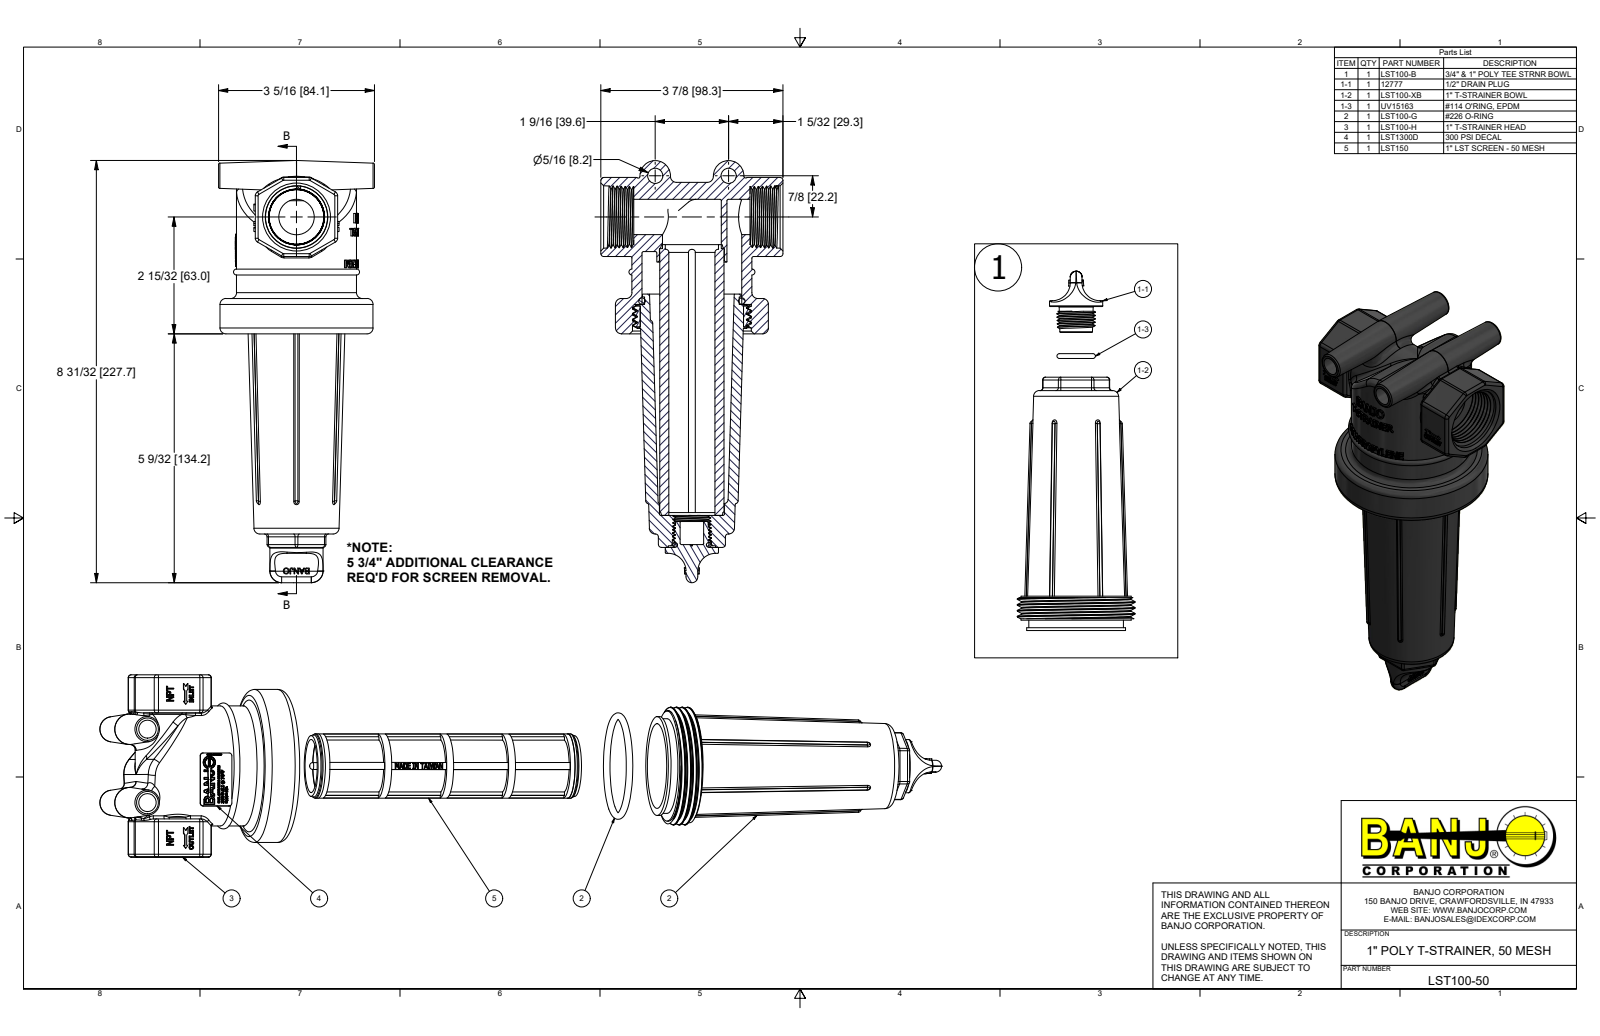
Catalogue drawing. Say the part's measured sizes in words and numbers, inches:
The part is named "LST100-50; CE050D; LST100-B; LST100-XB (+6 more)". Its 3-D file was written by "Autodesk Inventor 2018 (AUTOMOTIVE_DESIGN)". It is 9 solids with 2843 faces: 1572 planar, 255 cylindrical and 1016 other. Overall it measures 38.886 by 14.249 by 3.312 inches. Its volume is 19.13 cubic inches and its surface area 480.5 square inches. Round holes: 1 of diameter 0.181, 1 of diameter 0.257, 1 of diameter 0.5, 1 of diameter 0.75, 1 of diameter 0.98, 1 of diameter 1.005, 1 of diameter 1.1, 1 of diameter 1.25, 1 of diameter 1.38, 1 of diameter 2.12, 1 of diameter 2.195, 1 of diameter 2.396. Round bosses or shafts: 1 of diameter 3.25, 1 of diameter 2.55, 1 of diameter 2.5, 1 of diameter 2.34, 1 of diameter 2.1, 1 of diameter 2.01, 1 of diameter 1.49, 1 of diameter 1.47. Partial cylindrical surfaces (rounded edges, fillets, slot ends): 52 of radius 0.06, 11 of radius 0.03, 8 of radius 0.094, 4 of radius 0.075, 2 of radius 0.026, 2 of radius 0.033, 2 of radius 0.035, 2 of radius 0.063. The main face-to-face distances are 0.15, 1.75, 1.35, 1.2, 0.75, 0.25, 0.7, 1.5, 4.45, 0.625.
